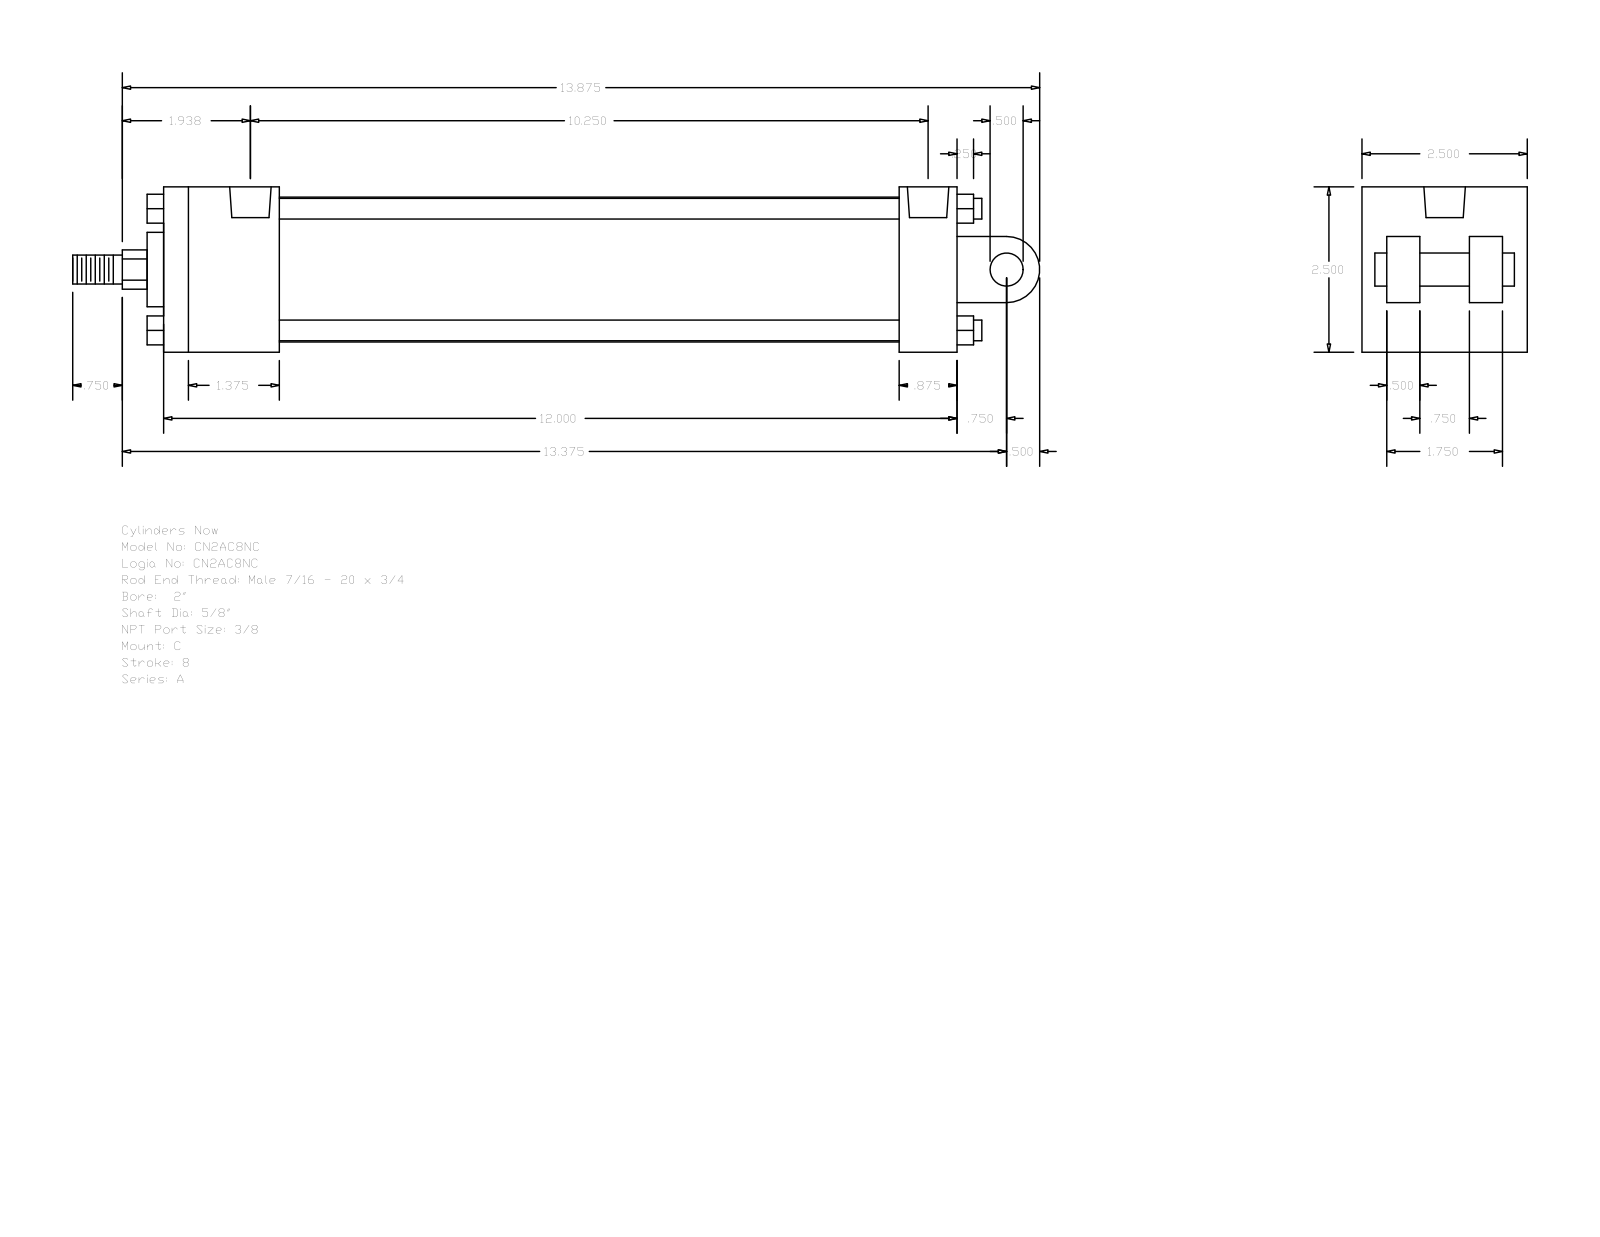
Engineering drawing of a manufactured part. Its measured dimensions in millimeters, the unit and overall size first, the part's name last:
Units: millimetres
Overall size (bounding box): 371.48 × 63.5 × 63.5
Round holes (diameter × count): ⌀5.56 ×4, ⌀15.93 ×2
Round bosses / shafts (diameter × count): ⌀7.94 ×4, ⌀55.63 ×1, ⌀28.57 ×1, ⌀15.88 ×1, ⌀12.7 ×1, ⌀11.11 ×1
Partial cylindrical surfaces — rounded edges, fillets, slot ends (radius × count): R7.54 ×1, R12.7 ×1
Main face-to-face distances: 63.5, 304.8, 44.45, 9.52, 260.35, 282.57, 238.12, 22.23, 12.7, 53.98
Hole centre spacings: 252.4, 3.97, 3.98, 256.37, 256.38, 260.35
Bodies: 0 solids, 135 faces (102 planar, 33 cylindrical, 0 other)
Part name (STEP PRODUCT): A_C__0200_0.625
STEP written by: GSSL Pune (CONFIG_CONTROL_DESIGN)
